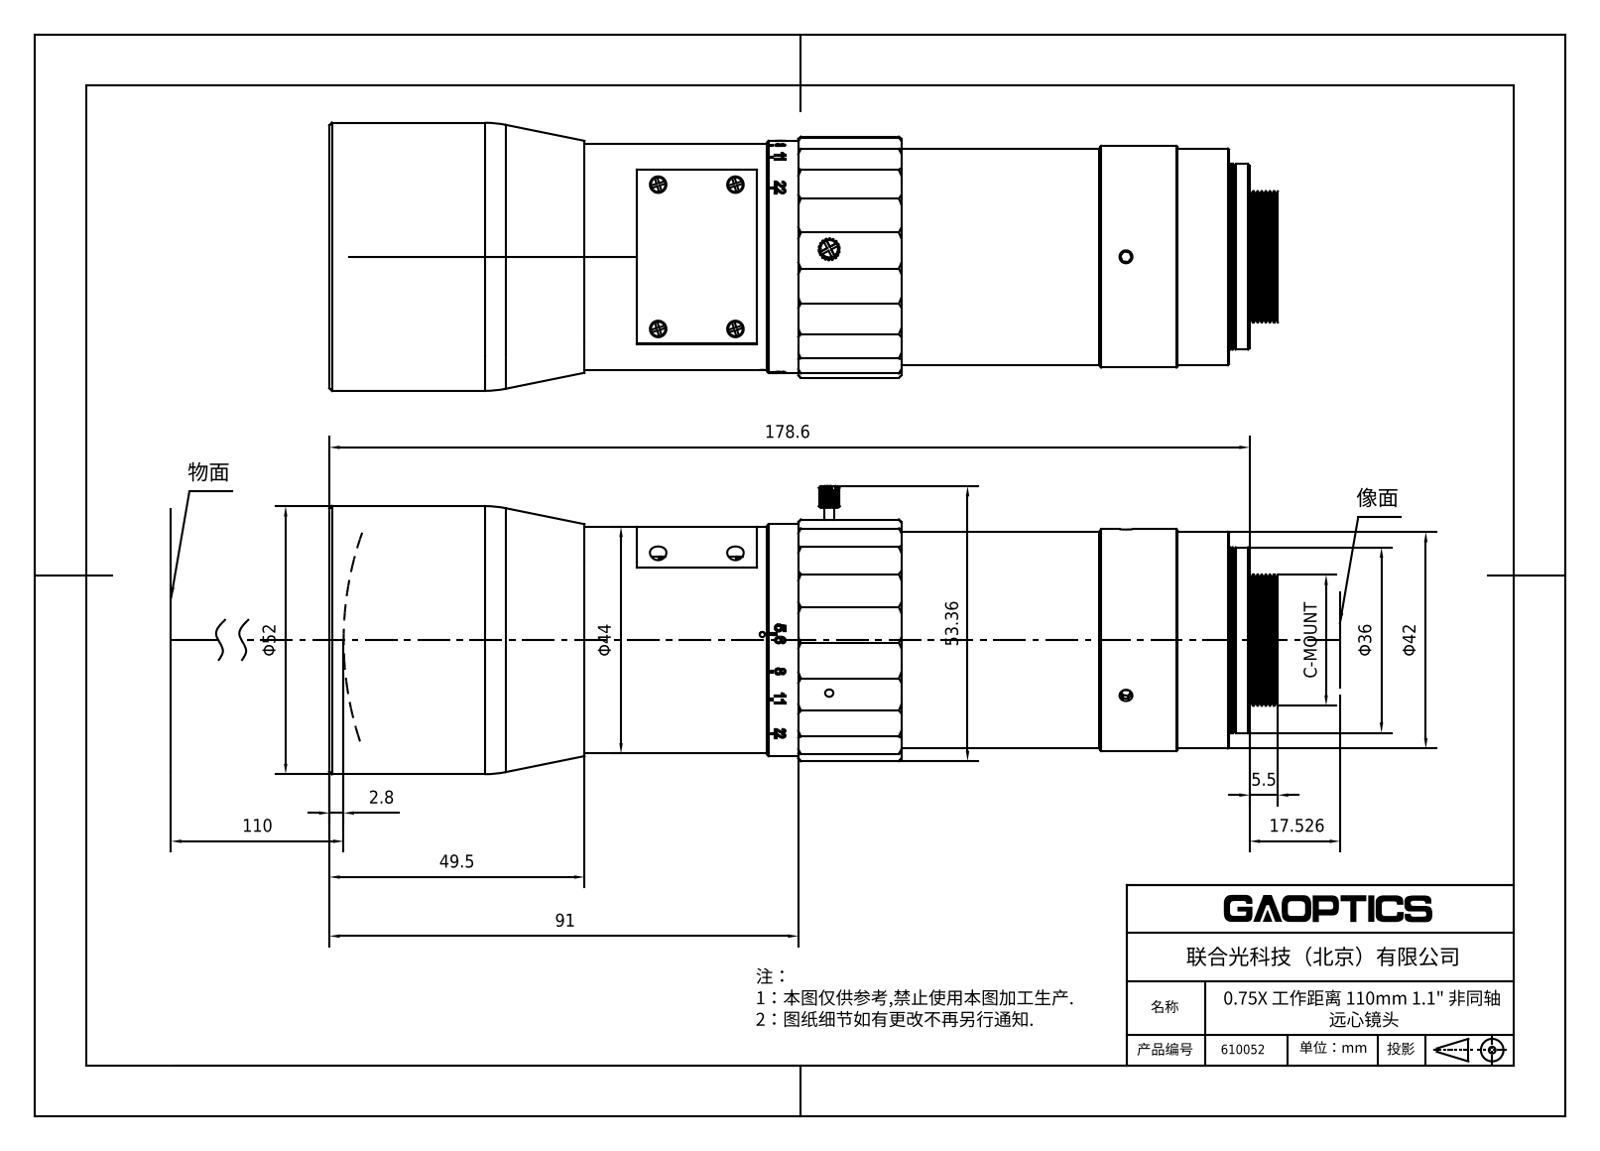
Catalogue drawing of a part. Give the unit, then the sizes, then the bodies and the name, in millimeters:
Units: millimetres
Overall size (bounding box): 184.08 × 45.5 × 45.5
Round holes (diameter × count): ⌀1.01 ×16, ⌀1.43 ×8, ⌀1.6 ×8, ⌀2.2 ×4, ⌀3.2 ×4, ⌀2.5 ×3, ⌀2 ×1, ⌀3.5 ×1, ⌀9.1 ×1, ⌀13.8 ×1, ⌀14.9 ×1, ⌀15.7 ×1
Round bosses / shafts (diameter × count): ⌀1.4 ×16, ⌀1 ×16, ⌀45.5 ×1, ⌀43.5 ×1, ⌀43 ×1, ⌀42 ×1, ⌀41 ×1, ⌀40 ×1
Partial cylindrical surfaces — rounded edges, fillets, slot ends (radius × count): R0.5 ×43, R12.5 ×21, R0.2 ×20, R2.3 ×16, R0.72 ×8, R4.9 ×8, R9.5 ×8, R1.25 ×4
Main face-to-face distances: 20, 89.58, 6.49, 3.7, 4, 39.77, 27.5, 117.08, 1.6, 21.6
Hole centre spacings: 4.15, 5.51, 5.9, 7.2, 8.5, 10.05, 10.18, 10.9
Volume: 142 247 mm³ · Surface area: 108 630 mm²
Bodies: 48 solids, 1385 faces (362 planar, 637 cylindrical, 386 other)
Part name (STEP PRODUCT): 0.75x -3l xin20240719
STEP written by: SolidWorks 2016 (AUTOMOTIVE_DESIGN)
